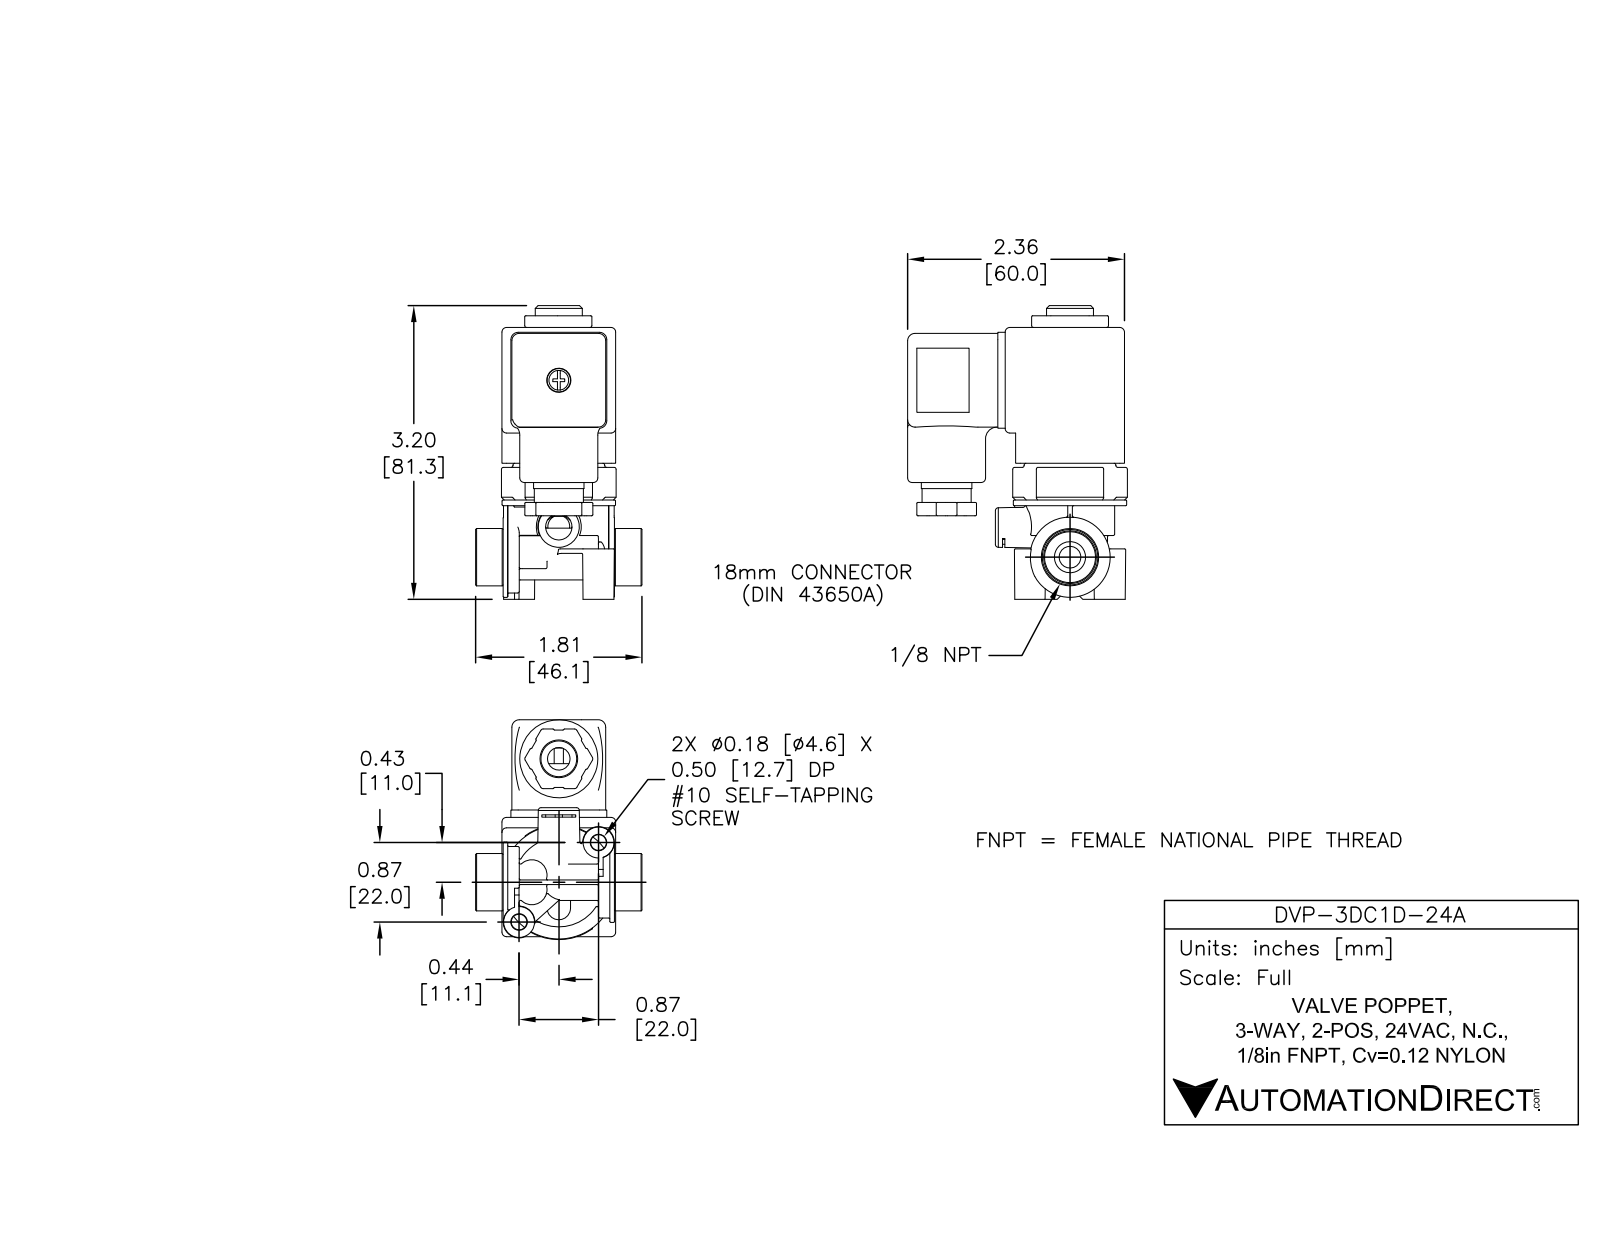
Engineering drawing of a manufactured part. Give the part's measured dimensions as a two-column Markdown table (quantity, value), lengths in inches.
| quantity | value |
| --- | --- |
| part name | DVP-3DC1D-24A |
| STEP written by | SolidWorks 2015 (AUTOMOTIVE_DESIGN) |
| units | inches |
| bodies | 10 solids, 2067 faces (823 planar, 396 cylindrical, 848 other) |
| overall size | 3.204 × 2.395 × 1.813 |
| volume | 4.004 in³ |
| surface area | 57.76 in² |
| round holes (diameter × count) | 0.06 × 2, 0.236 × 2, 0.339 × 2, 0.08 × 1, 0.093 × 1, 0.102 × 1, 0.12 × 1, 0.137 × 1, 0.203 × 1, 0.245 × 1, 0.263 × 1, 0.287 × 1 |
| round bosses / shafts (diameter × count) | 0.29 × 2, 1.236 × 1, 1 × 1, 0.972 × 1, 0.922 × 1, 0.89 × 1, 0.875 × 1, 0.85 × 1 |
| partial cylindrical surfaces (radius × count) | 0.01 × 85, 0.015 × 50, 0.05 × 21, 0.02 × 12, 0.08 × 12, 0.026 × 6, 0.03 × 6, 0.04 × 4 |
| main face-to-face distances | 1.083, 1.24, 0.048, 0.157, 0.925, 1.48, 0.109, 1.131, 0.974, 1.367 |
| hole center spacings | 0.281, 0.283, 1.062, 1.343, 1.345, 1.612, 1.626, 2.184 |
